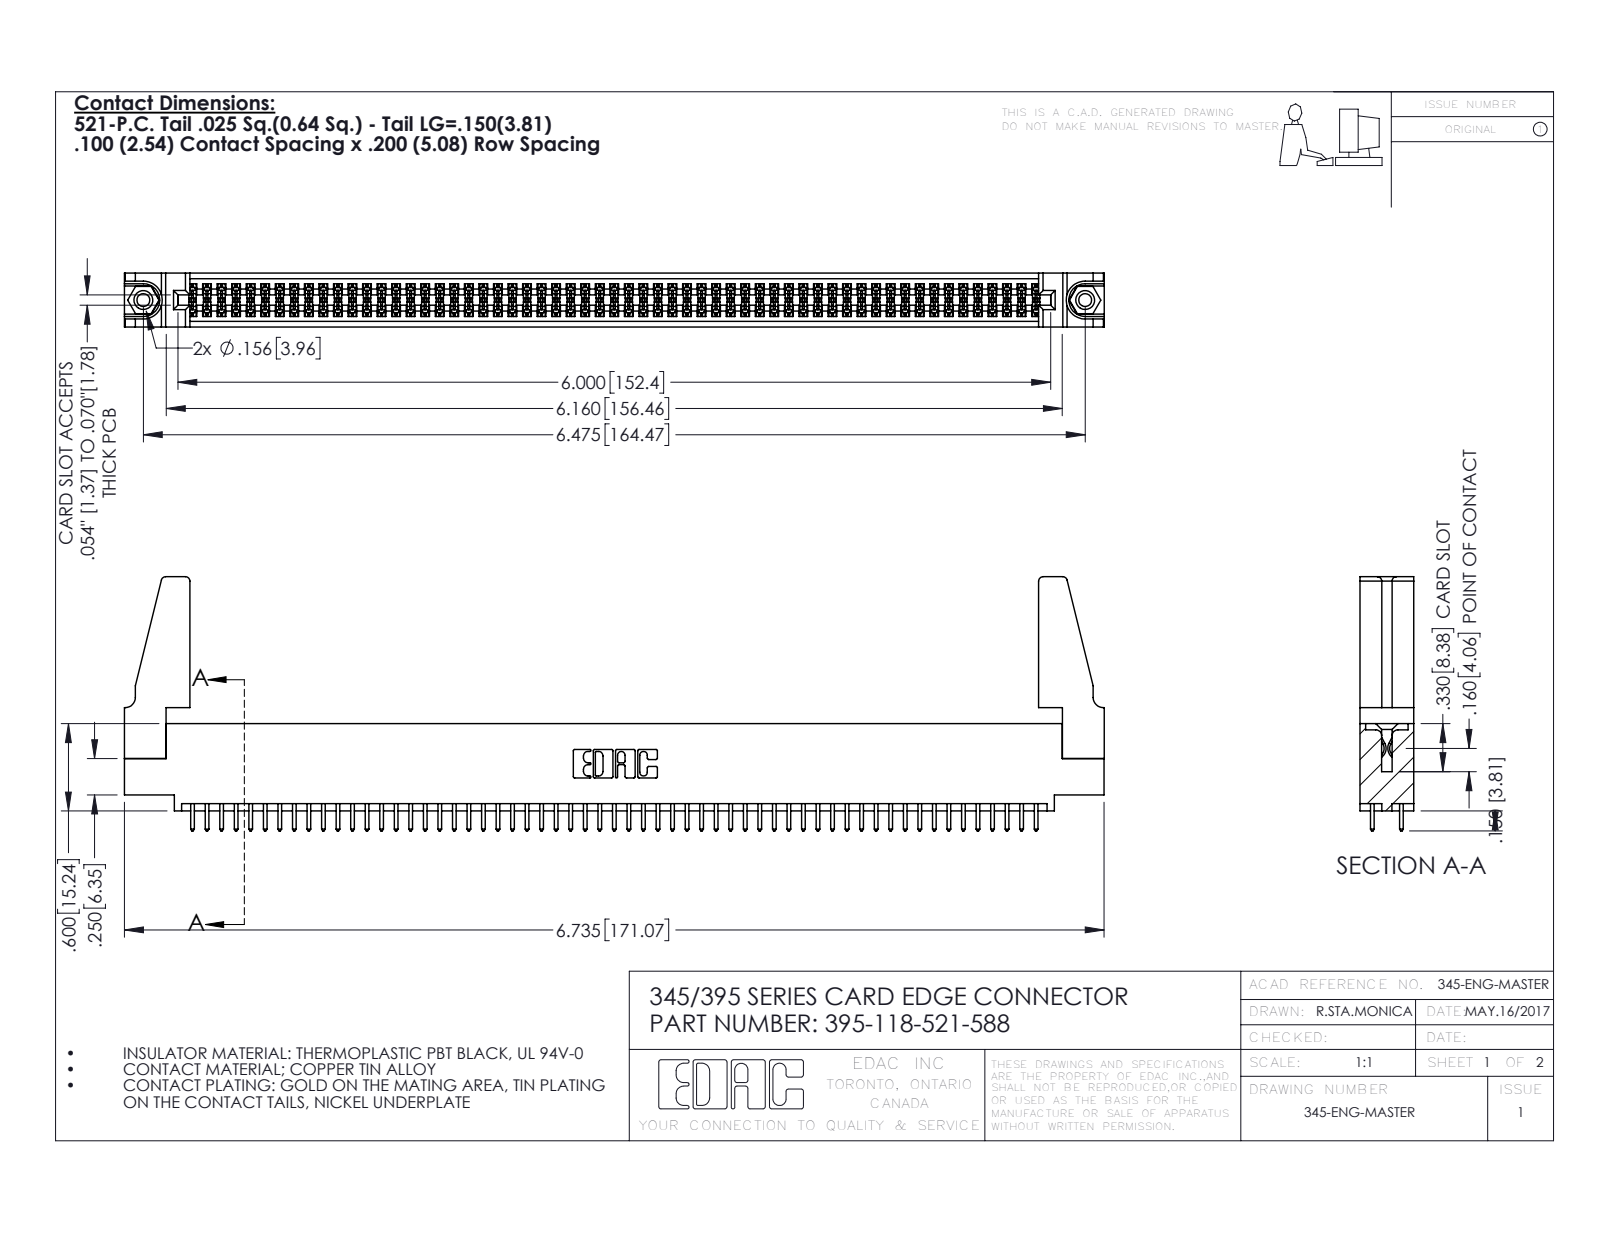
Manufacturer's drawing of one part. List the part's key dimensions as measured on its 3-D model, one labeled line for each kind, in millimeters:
Part name (STEP PRODUCT): 345-292-001_345-293-121; 345-220-078_345-220-088; 395-118-521-588; 345-250-001_345-250-001-102 (+1 more)
STEP written by: SolidWorks 2016 (CONFIG_CONTROL_DESIGN)
Units: millimetres
Bodies: 123 solids, 6154 faces (4050 planar, 2088 cylindrical, 16 other)
Overall size (bounding box): 171.1 × 44.4 × 9.4
Volume: 19 910 mm³ · Surface area: 27 850 mm²
Round holes (diameter × count): ⌀2.3 ×2, ⌀3.2 ×2, ⌀4 ×2, ⌀1.6 ×1
Round bosses / shafts (diameter × count): ⌀3.9 ×2
Partial cylindrical surfaces — rounded edges, fillets, slot ends (radius × count): R0.2 ×177, R0.3 ×118, R0.3 ×22, R0.8 ×8, R0.2 ×6, R0.8 ×6, R0.7 ×3, R0.4 ×2
Main face-to-face distances: 1.8, 7.6, 9.4, 5.1, 2.5, 6.9, 0.6, 5.7, 4.4, 3.8
Hole centre spacings: 6.9, 158.5, 164.5
